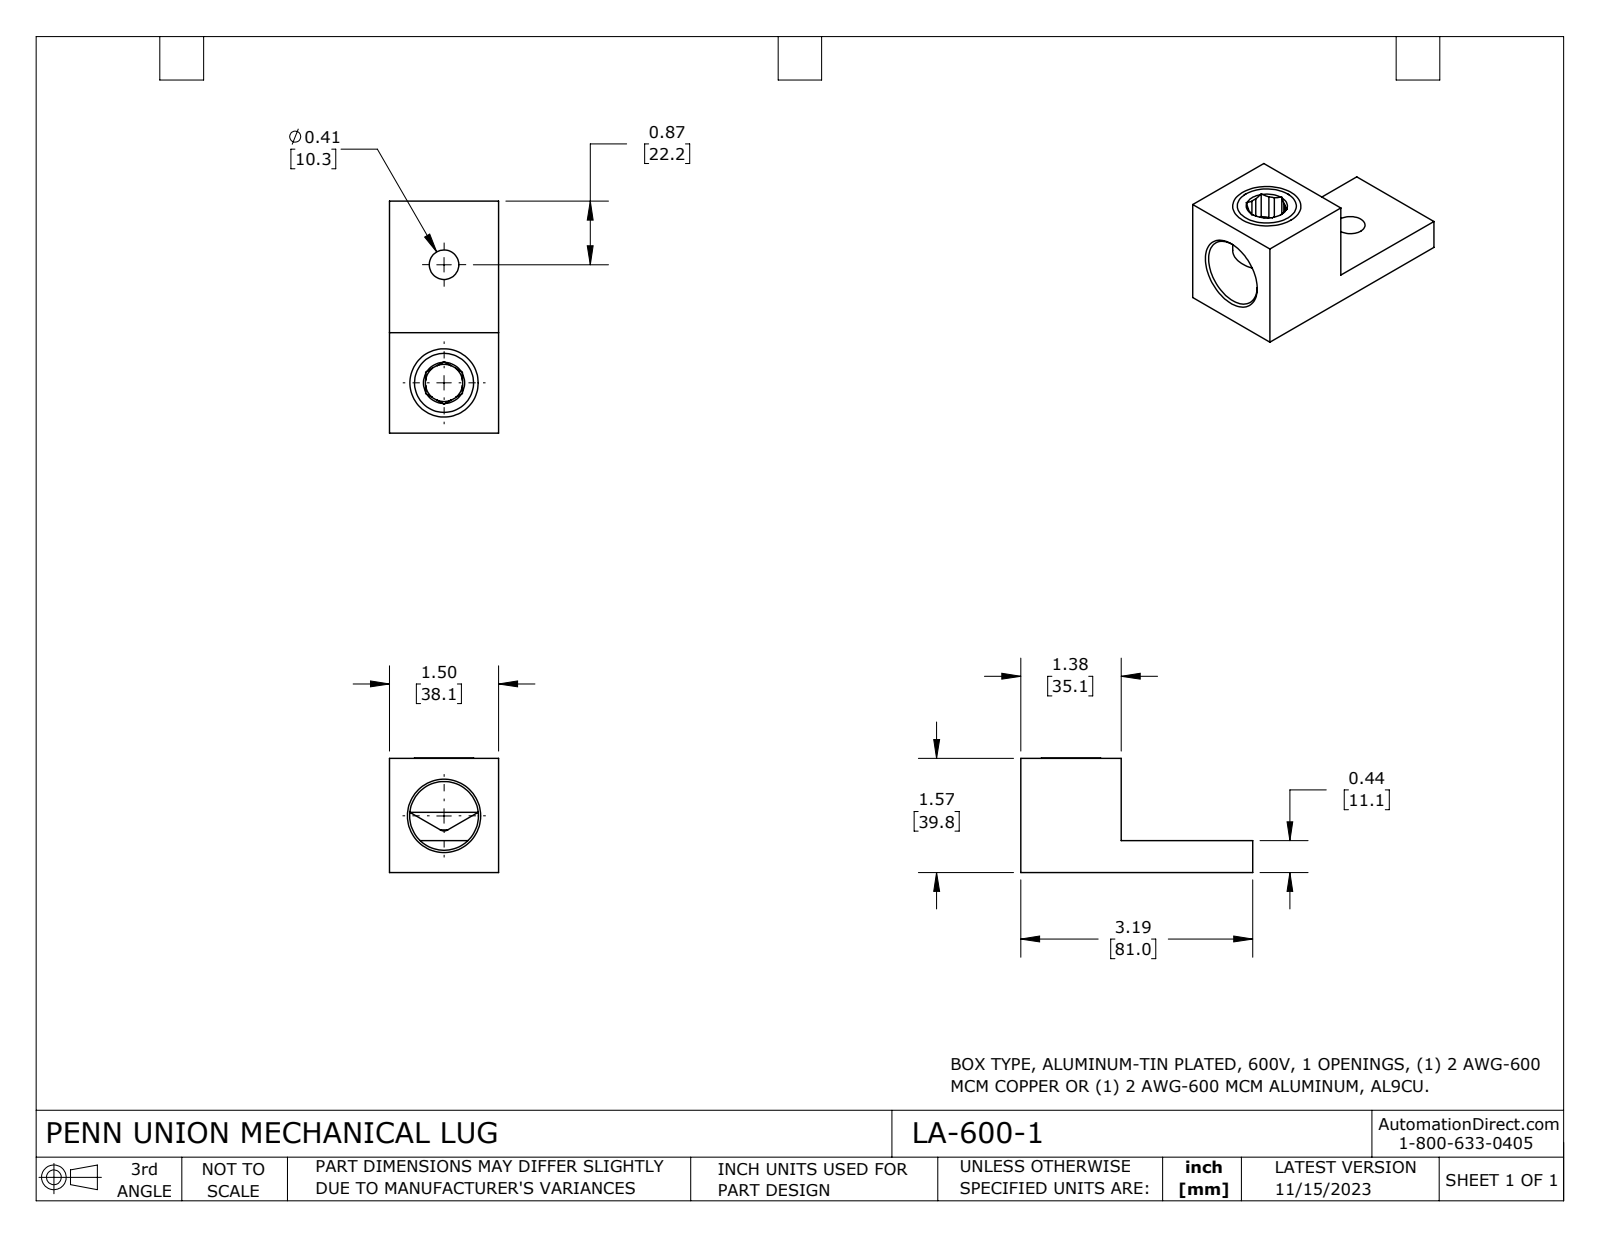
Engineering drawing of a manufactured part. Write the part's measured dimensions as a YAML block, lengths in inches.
part_name: "LA-600-1"
step_written_by: "SolidWorks 2023 (CONFIG_CONTROL_DESIGN)"
units: inches
bodies: {solids: 2, faces: 56, planar: 28, cylindrical: 10, other: 18}
overall_size: [3.189, 1.571, 1.5]
volume: 3.629
surface_area: 27.55
round_holes:
  - {diameter: 0.406, count: 1}
  - {diameter: 0.512, count: 1}
  - {diameter: 0.875, count: 1}
  - {diameter: 0.945, count: 1}
round_bosses_or_shafts:
  - {diameter: 0.937, count: 1}
face_to_face_distances: [1.5, 0.437, 1.567, 1.13, 1.382, 3.189, 1.807, 1.571, 1.134, 0.497]
hole_center_spacings: [1.624]
